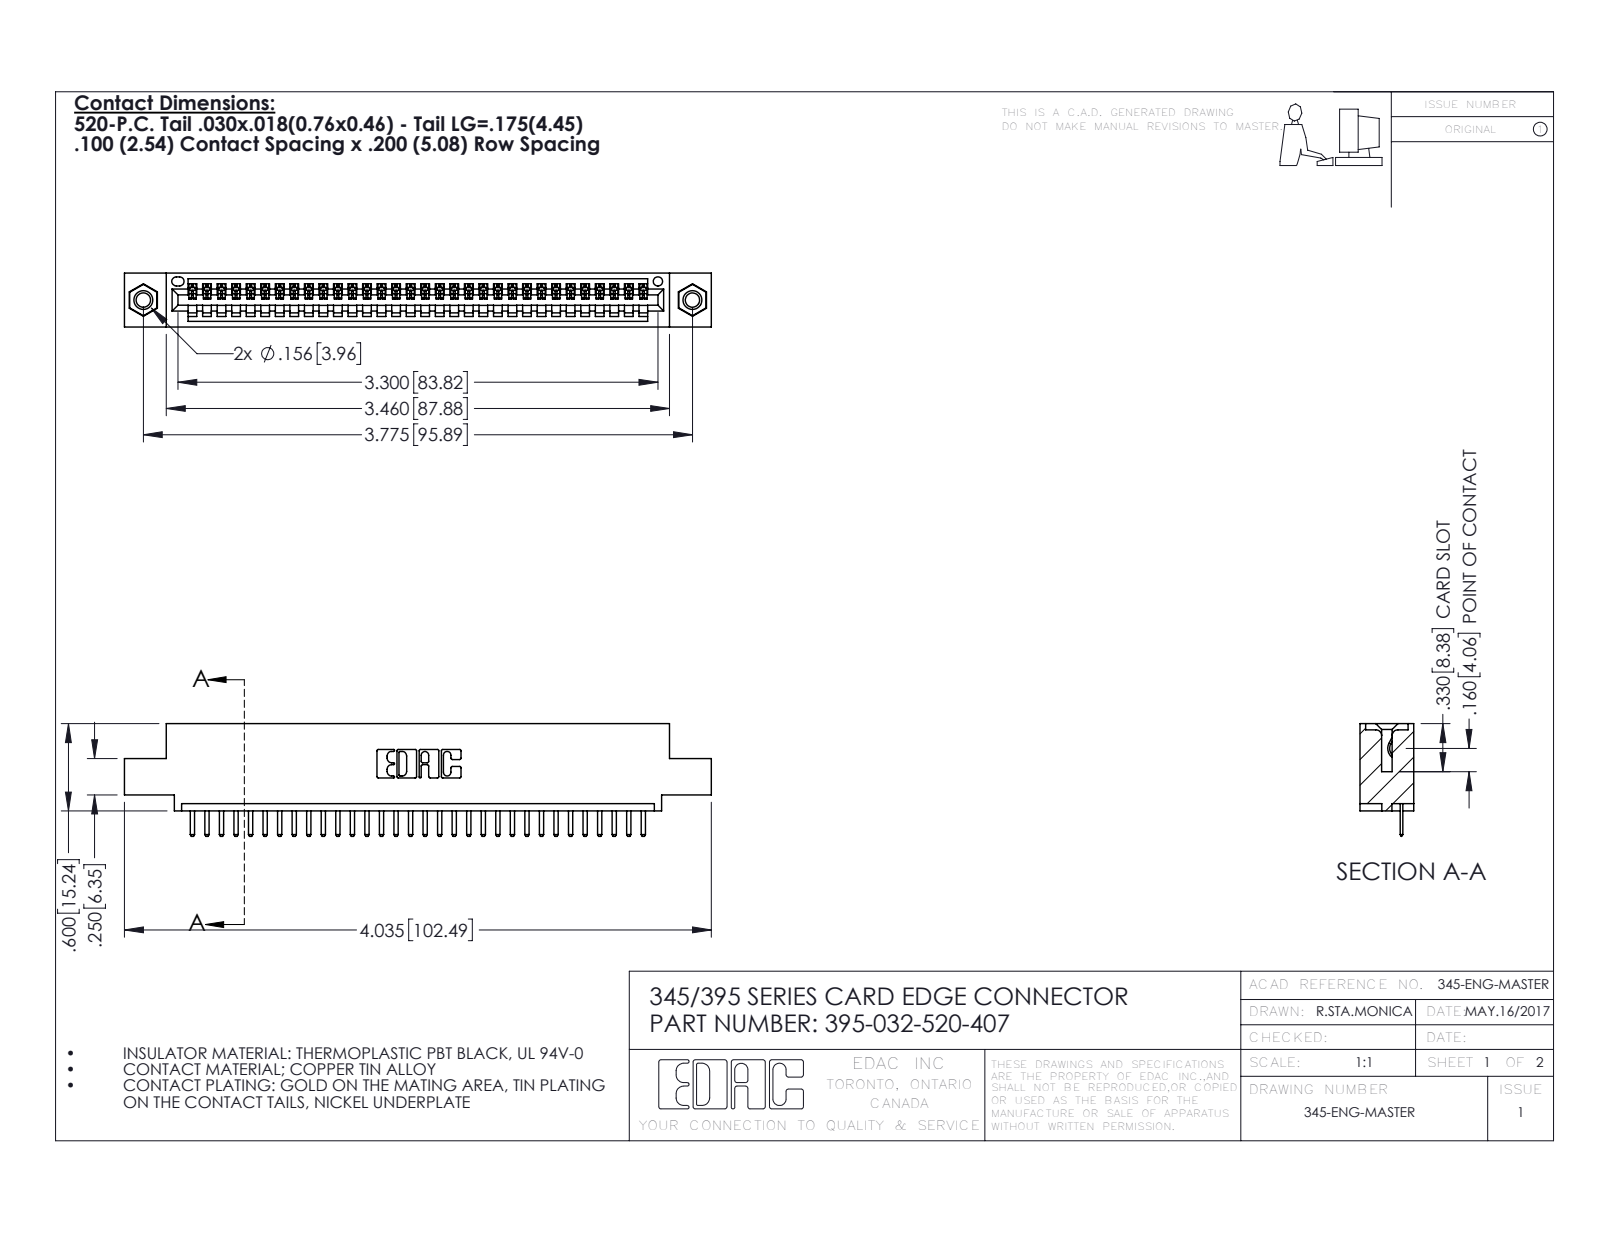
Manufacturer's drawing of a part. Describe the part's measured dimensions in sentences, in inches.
The part is named "395-032-520-407; 345 Part_0.110 Offset - 0.156 Dia-TI; 345-250-001_345-250-005-103; 345-292-001_345-293-120". Its 3-D file was written by "SolidWorks 2016 (CONFIG_CONTROL_DESIGN)". It is 35 solids with 2174 faces: 1460 planar, 698 cylindrical and 16 other. Overall it measures 4.035 by 0.775 by 0.37 inches. Its volume is 0.578 cubic inches and its surface area 19.01 square inches. Round holes: 2 of diameter 0.098, 2 of diameter 0.125, 2 of diameter 0.156, 1 of diameter 0.064. Round bosses or shafts: 2 of diameter 0.155. Partial cylindrical surfaces (rounded edges, fillets, slot ends): 66 of radius 0.01, 64 of radius 0.006, 22 of radius 0.01, 6 of radius 0.007, 6 of radius 0.031, 3 of radius 0.026, 2 of radius 0.031, 2 of radius 0.04. The main face-to-face distances are 0.072, 0.298, 0.37, 0.2, 0.098, 0.272, 0.025, 0.225, 0.072, 0.149. The hole center spacings are 0.27, 3.54, 3.775.
